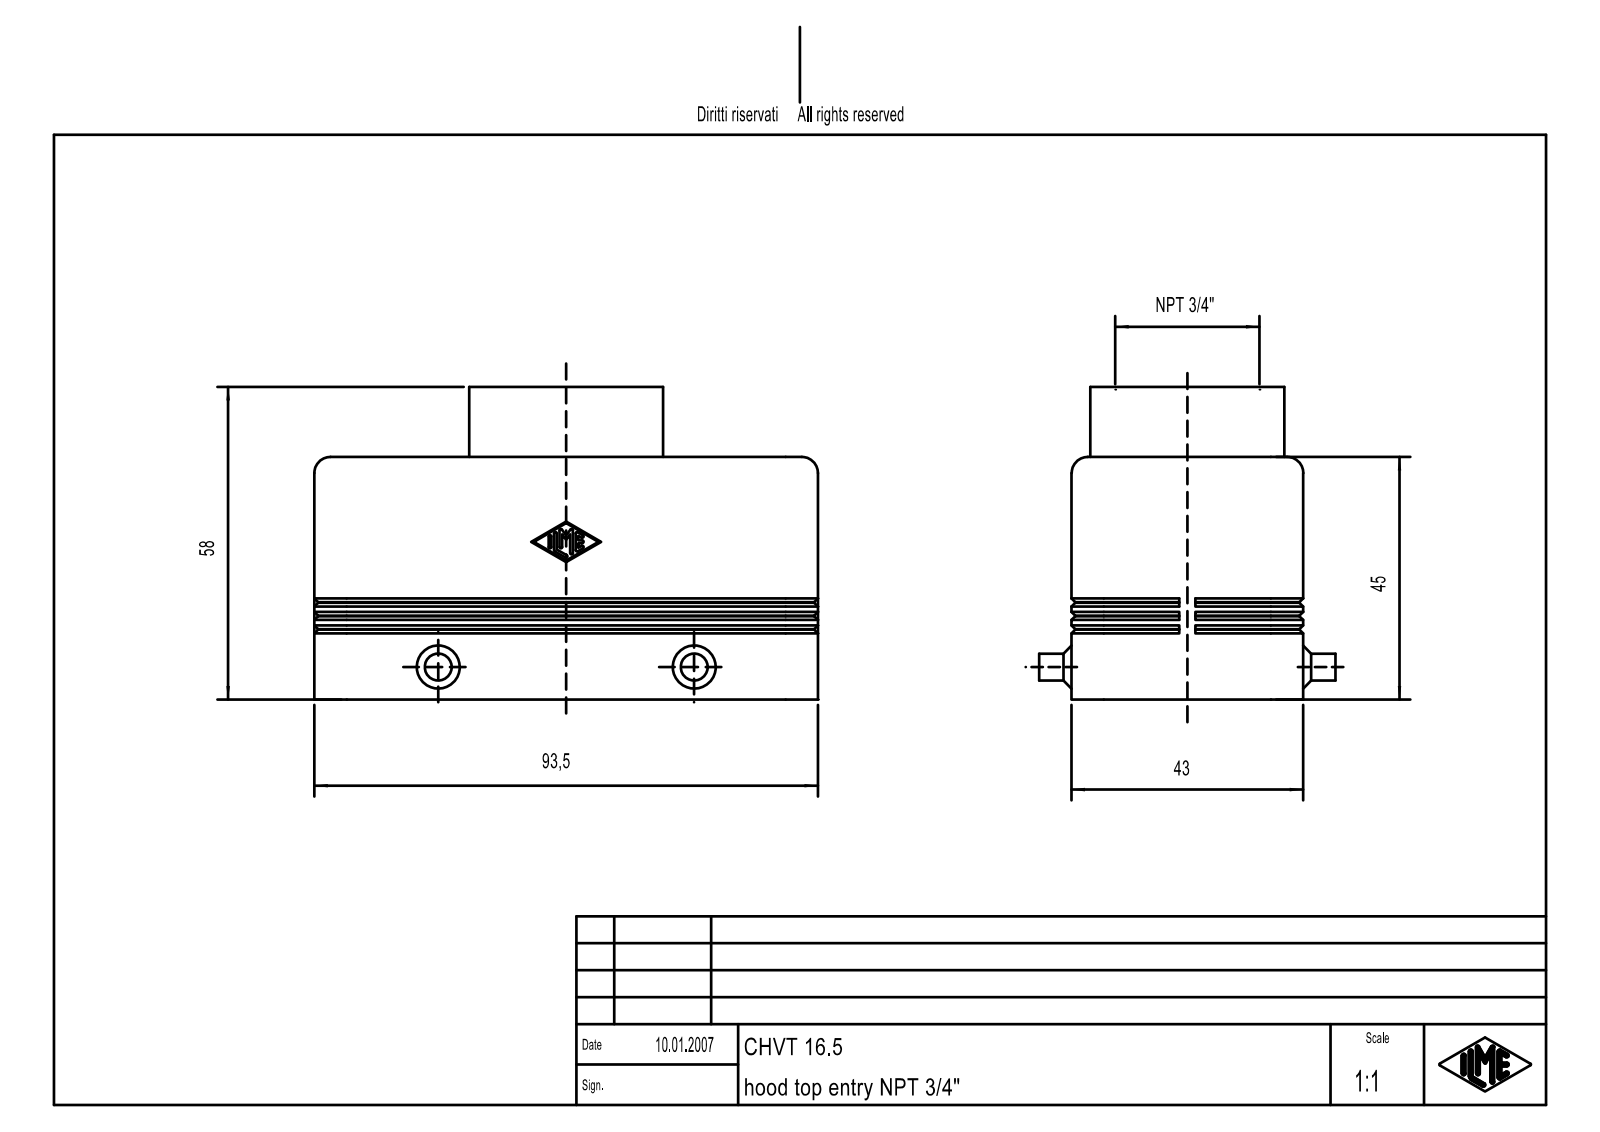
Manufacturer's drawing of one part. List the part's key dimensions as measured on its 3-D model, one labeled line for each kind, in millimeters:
Part name (STEP PRODUCT): MSBO5449
STEP written by: Creo Elements/Direct Modeling 18.0B 02-Dec-2011 (C) Parametric Technology GmbH (AUTOMOTIVE_DESIGN)
Units: millimetres
Bodies: 1 solid, 275 faces (147 planar, 82 cylindrical, 46 other)
Overall size (bounding box): 93.5 × 58 × 55
Volume: 59 382 mm³ · Surface area: 33 015 mm²
Round holes (diameter × count): ⌀4 ×4, ⌀2.46 ×3, ⌀2.46 ×1
Round bosses / shafts (diameter × count): ⌀5 ×2, ⌀36 ×1
Partial cylindrical surfaces — rounded edges, fillets, slot ends (radius × count): R0.25 ×14, R3 ×8, R2 ×4, R5.3 ×4, R6 ×4, R1.5 ×1
Main face-to-face distances: 3, 40, 37, 43, 11.5, 8.5, 90.5, 20, 93.5, 87.5
Hole centre spacings: 27, 77.5, 82.07
